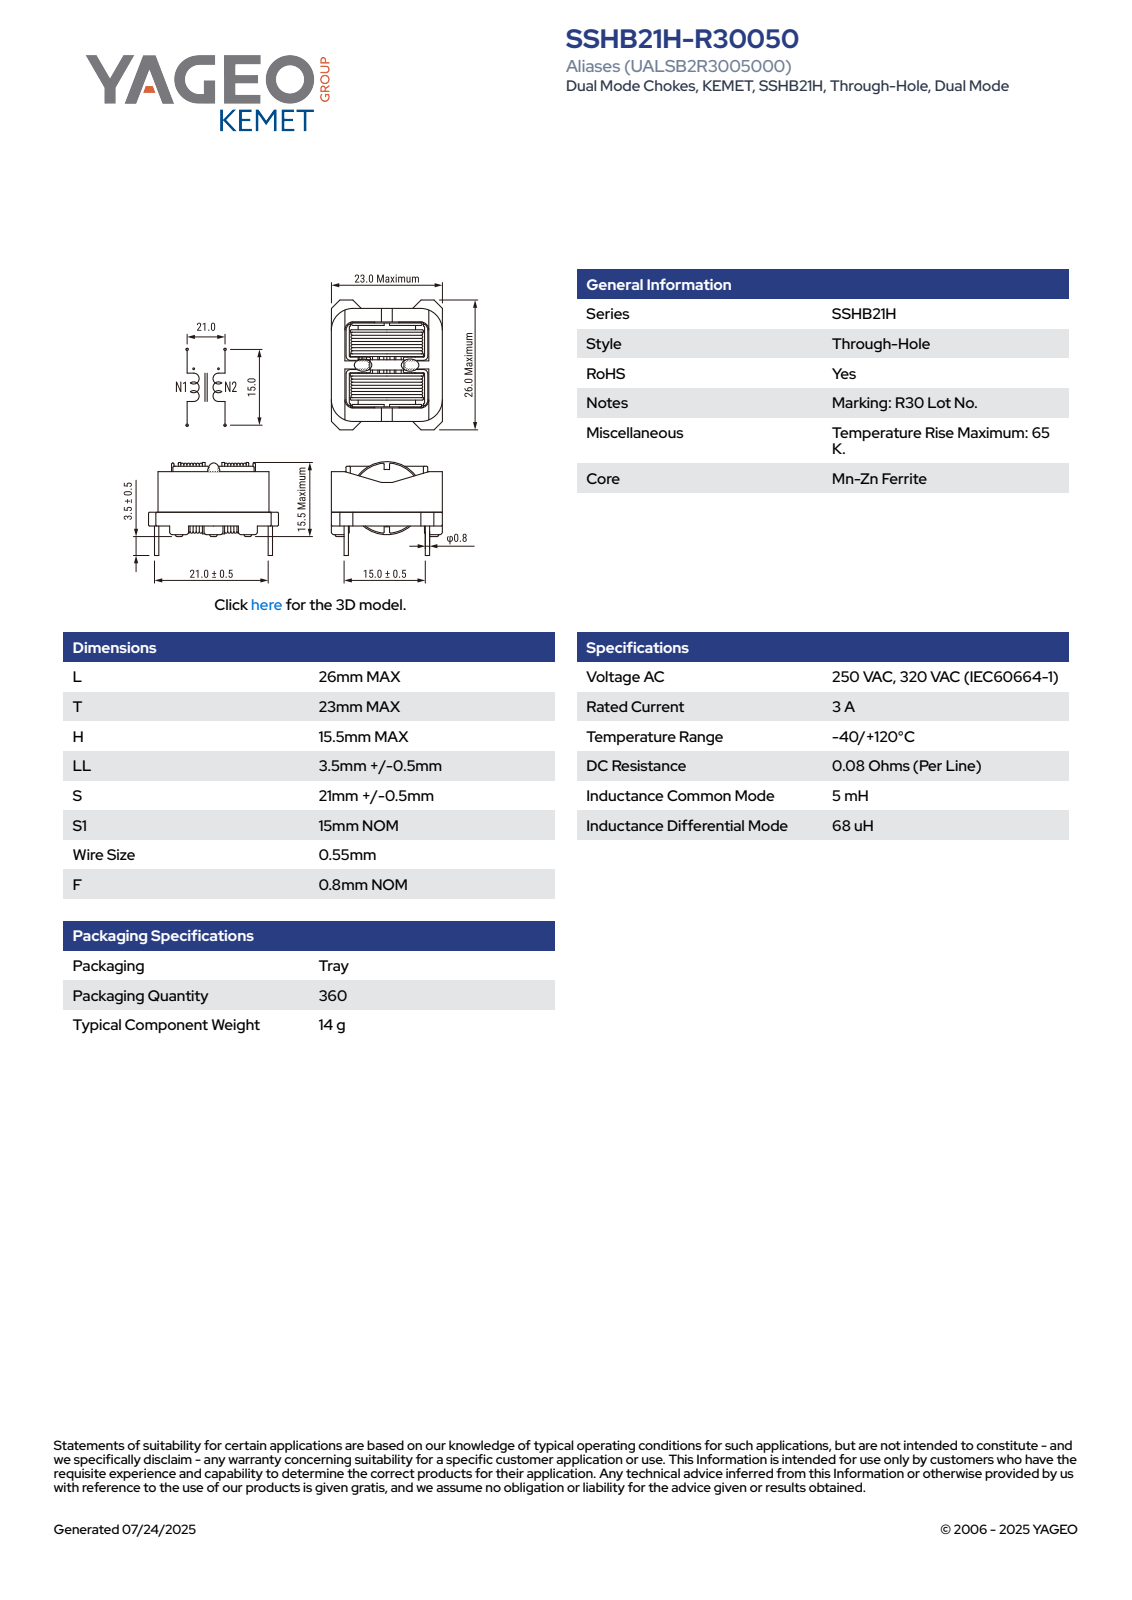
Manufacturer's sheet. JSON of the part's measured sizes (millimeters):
{"part_name": "SSHB21H(MAX-LOGO)", "step_written_by": "SolidWorks 2018 (AUTOMOTIVE_DESIGN)", "units": "millimeters", "bodies": {"solids": 1, "faces": 508, "planar": 340, "cylindrical": 110, "other": 58}, "overall_size": [26, 23, 19], "volume_mm3": 4556, "surface_area_mm2": 4911, "round_holes": [[5.4, 1]], "round_bosses_or_shafts": [[0.8, 4], [13.5, 1], [13, 1], [10.6, 1], [6.3, 1]], "partial_cylinders_radius": [[0.2, 22], [0.5, 10], [0.8, 8], [0.3, 4], [1.3, 4], [1.5, 4], [4, 4], [2.6, 1]], "face_to_face_distances": [0.6, 3.95, 0.65, 4.55, 18.45, 2.7, 8.9, 10.05, 0.8, 18.2]}
